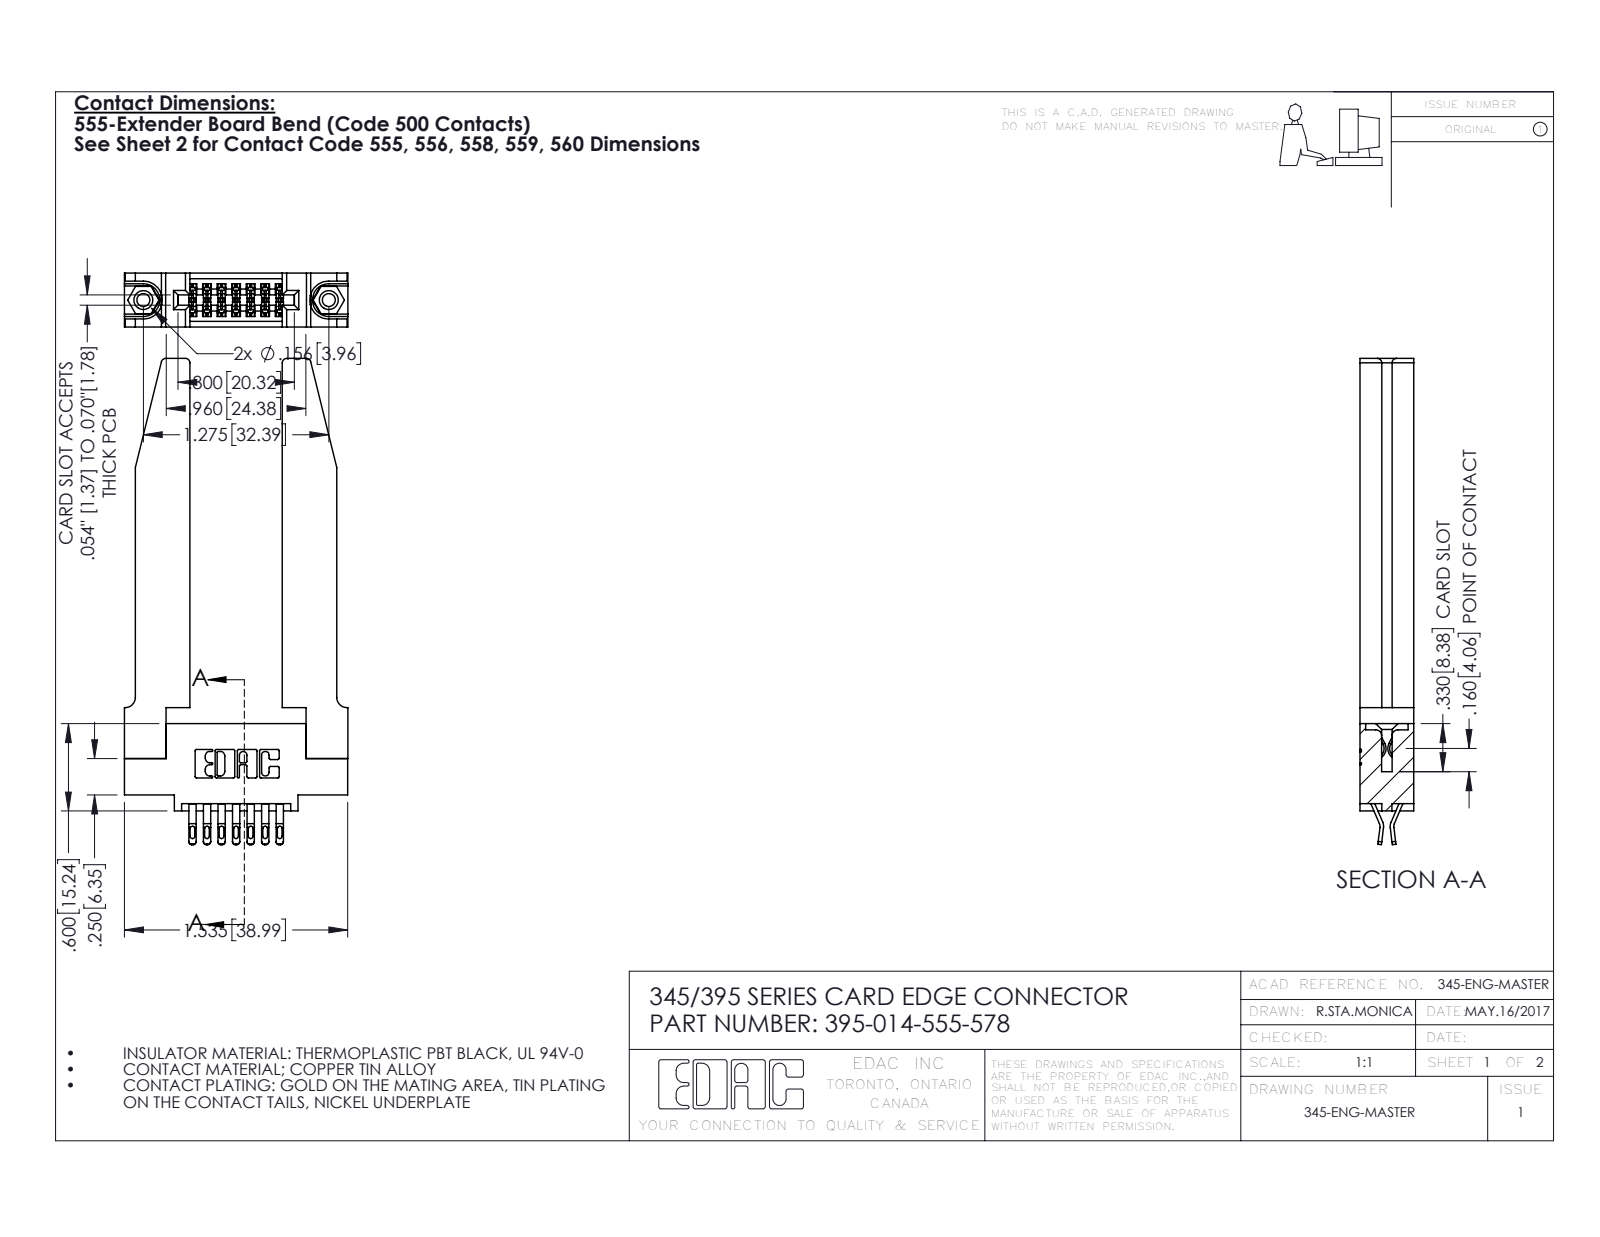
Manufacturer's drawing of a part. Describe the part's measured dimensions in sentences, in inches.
The part is named "345-292-001_555 Tail; 395-014-555-578; 345 Part_0.110 Offset - 0.156 Dia-TH; 345-250-001_345-250-001-102 (+1 more)". Its 3-D file was written by "SolidWorks 2016 (CONFIG_CONTROL_DESIGN)". It is 19 solids with 1148 faces: 660 planar, 436 cylindrical and 52 other. Overall it measures 3.342 by 1.536 by 0.37 inches. Its volume is 0.684 cubic inches and its surface area 17.78 square inches. Round holes: 2 of diameter 0.089, 2 of diameter 0.125, 2 of diameter 0.156, 1 of diameter 0.064. Round bosses or shafts: 2 of diameter 0.155. Partial cylindrical surfaces (rounded edges, fillets, slot ends): 35 of radius 0.016, 28 of radius 0.02, 22 of radius 0.01, 21 of radius 0.006, 8 of radius 0.03, 6 of radius 0.007, 6 of radius 0.031, 3 of radius 0.026. The main face-to-face distances are 0.37, 0.15, 0.072, 0.148, 0.22, 0.298, 0.077, 0.635, 0.071, 0.025. The hole center spacings are 0.27, 1.045, 1.275.
